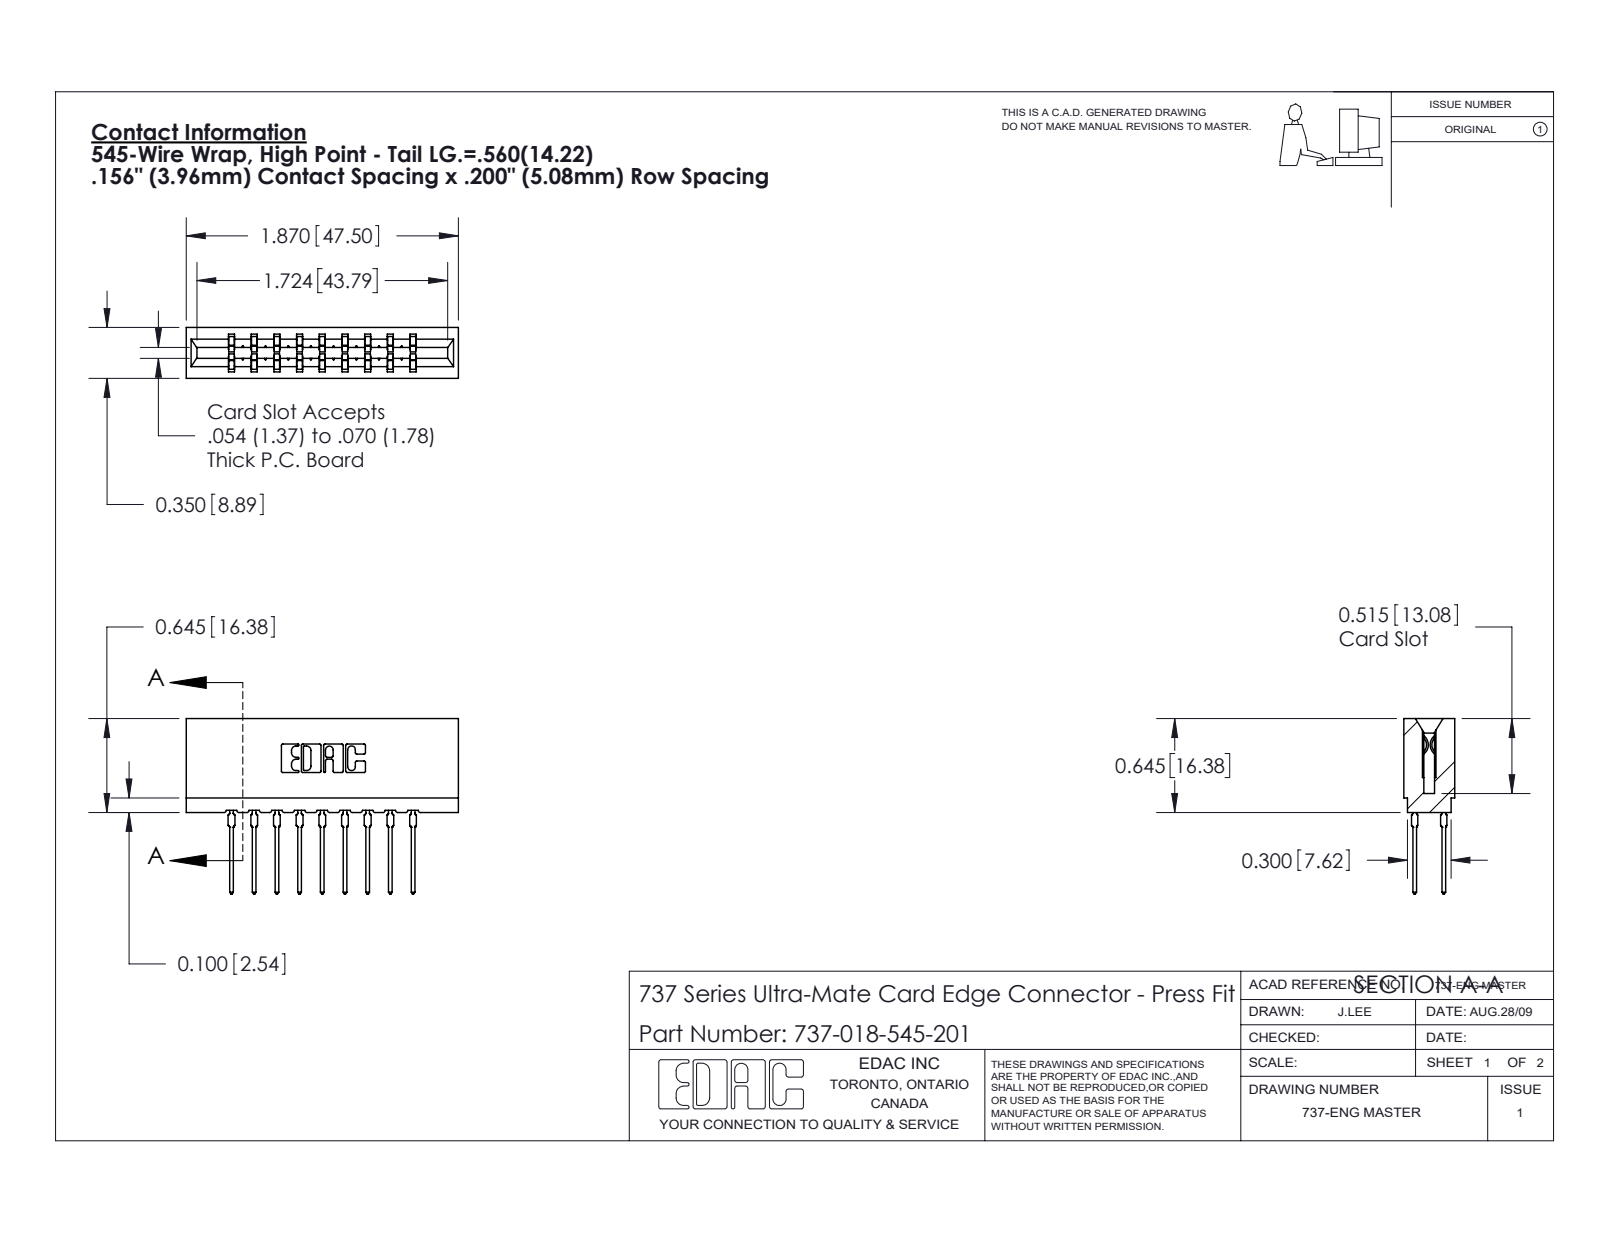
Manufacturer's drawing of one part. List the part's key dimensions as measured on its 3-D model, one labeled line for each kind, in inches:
Part name (STEP PRODUCT): 737-018-545-201; 737 Part_Insulator Option - 01; 745-292-001_545
STEP written by: SolidWorks 2020 (CONFIG_CONTROL_DESIGN)
Units: inches
Bodies: 19 solids, 1714 faces (891 planar, 355 cylindrical, 468 other)
Overall size (bounding box): 1.87 × 1.206 × 0.35
Volume: 0.303 in³ · Surface area: 10.53 in²
Partial cylindrical surfaces — rounded edges, fillets, slot ends (radius × count): R0.021 ×36, R0.01 ×22, R0.015 ×18, R0.005 ×8, R0.011 ×8, R0.007 ×6, R0.031 ×6, R0.026 ×3
Main face-to-face distances: 0.156, 0.138, 0.212, 0.624, 0.35, 0.312, 0.468, 0.354, 0.78, 0.198
